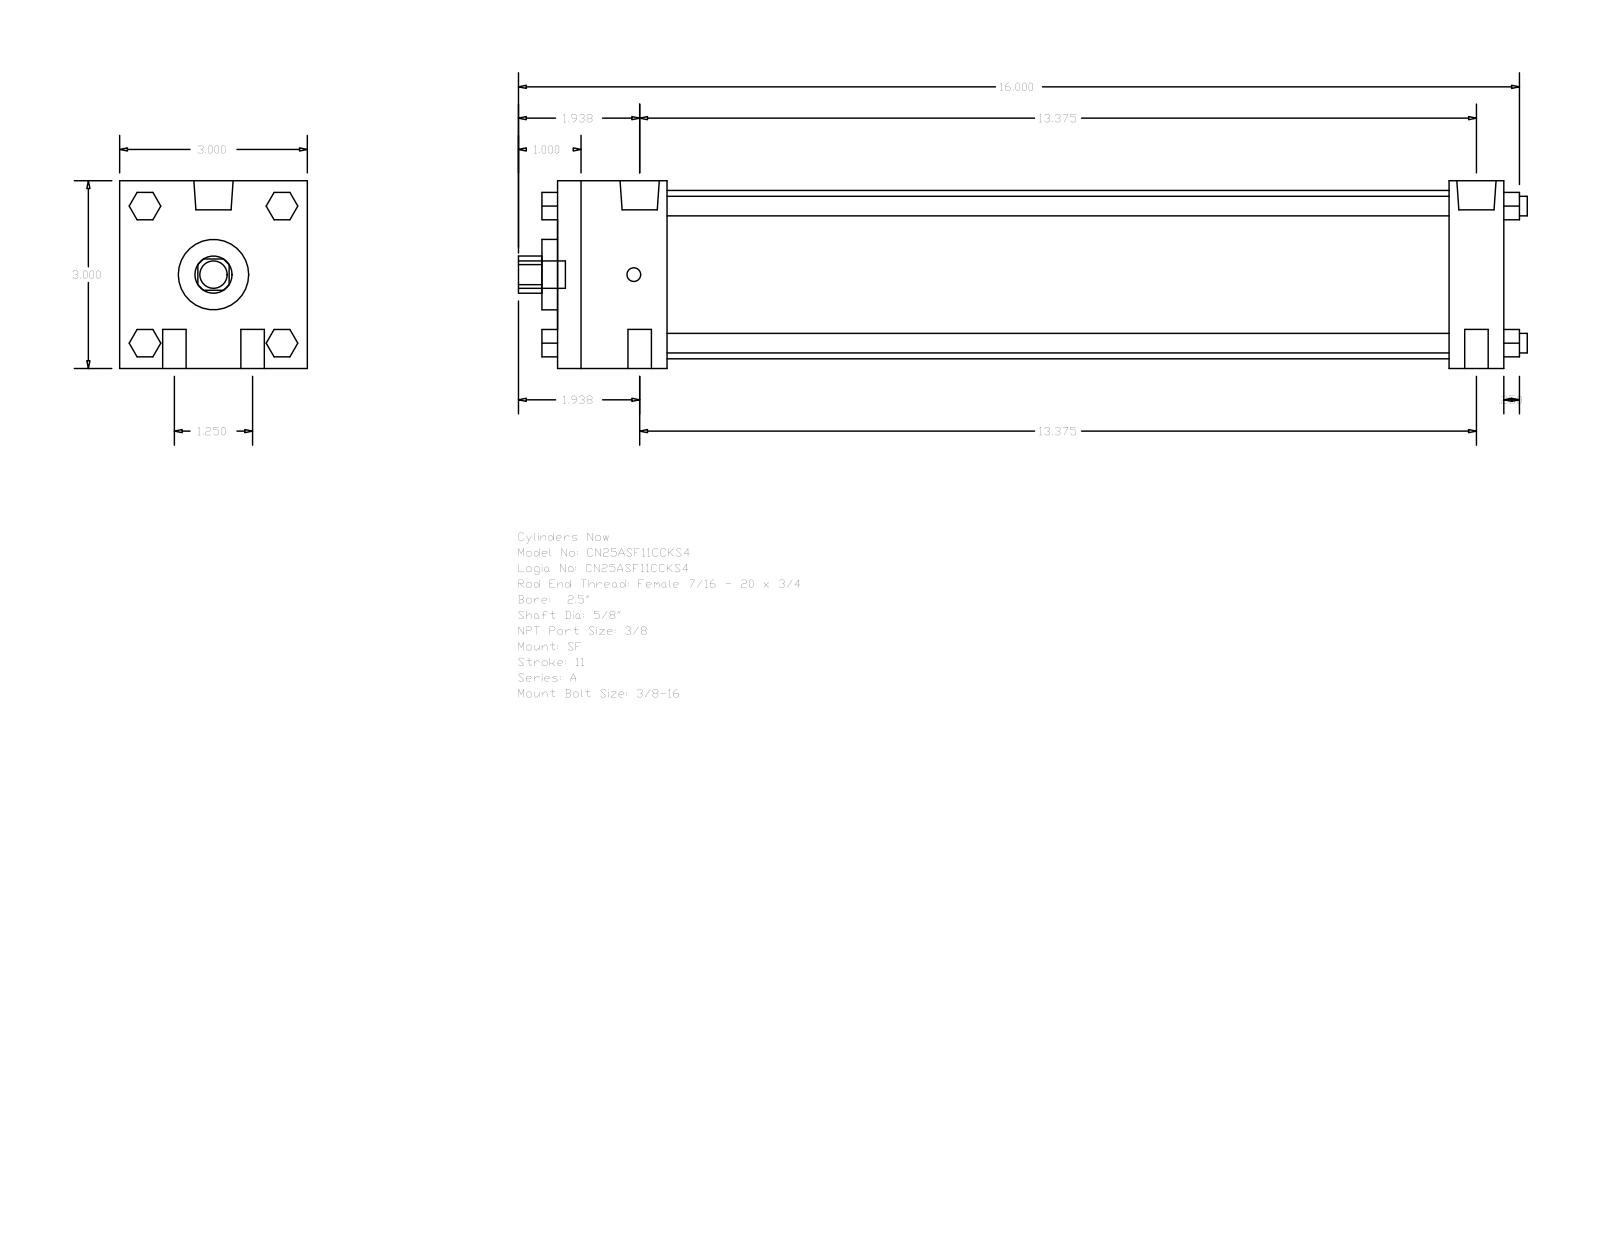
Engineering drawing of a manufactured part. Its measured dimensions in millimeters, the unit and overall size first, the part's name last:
Units: millimetres
Overall size (bounding box): 409.57 × 76.2 × 76.2
Round holes (diameter × count): ⌀15.88 ×1, ⌀28.57 ×1, ⌀68.33 ×1
Round bosses / shafts (diameter × count): ⌀9.53 ×4, ⌀7.94 ×4, ⌀15.93 ×2, ⌀5.56 ×2, ⌀11.11 ×1
Partial cylindrical surfaces — rounded edges, fillets, slot ends (radius × count): R7.54 ×1
Main face-to-face distances: 76.2, 384.17, 44.45, 361.94, 22.23, 317.49, 339.72, 390.52, 6.35, 50.8
Bodies: 0 solids, 124 faces (94 planar, 30 cylindrical, 0 other)
Part name (STEP PRODUCT): A_SF__0250_0.625
STEP written by: GSSL Pune (CONFIG_CONTROL_DESIGN)
